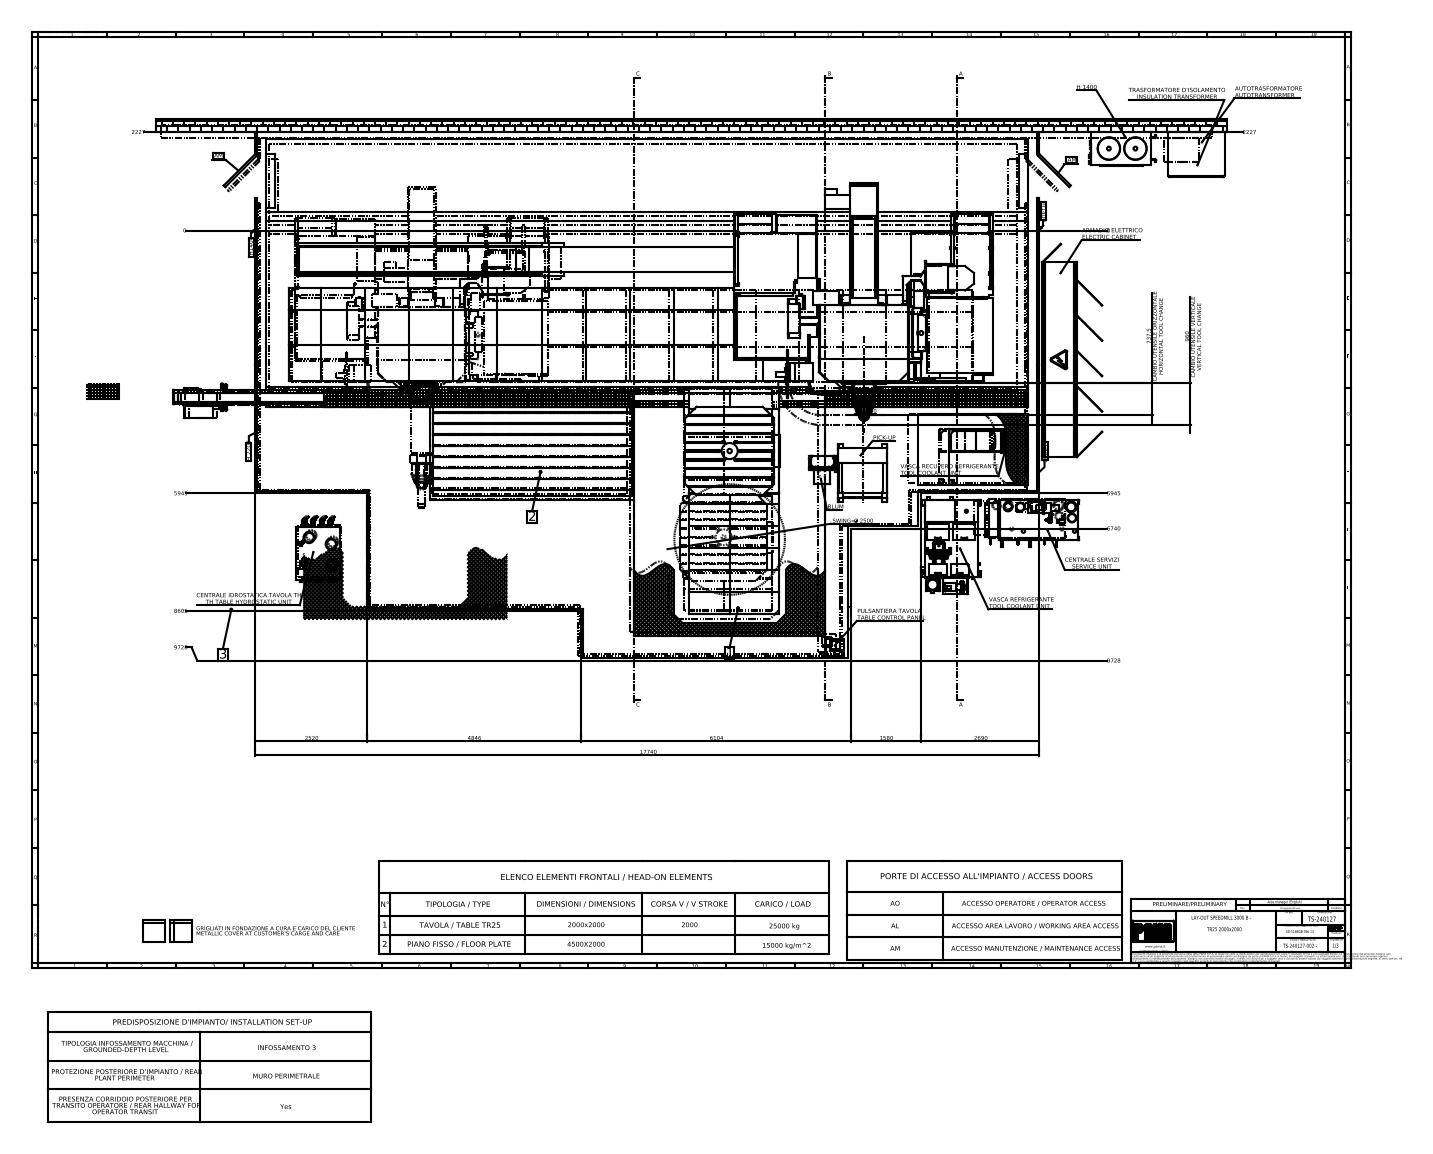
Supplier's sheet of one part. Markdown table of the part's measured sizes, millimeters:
| quantity | value |
| --- | --- |
| part name | S003552_X=MIN; Y=MIN; Z=MIN; W=MIN; S003085_Lato PO - Inf. 2-3; S001797_2000x2000 (PASSO CAVA = 200) SM. 250x250; S003390 (+8 more) |
| STEP written by | SolidWorks 2023 (AUTOMOTIVE_DESIGN) |
| units | millimeters |
| bodies | 448 solids, 6485 faces (5053 planar, 1070 cylindrical, 362 other) |
| overall size | 24240 × 15205 × 9400 |
| volume | 706 900 000 000 mm³ |
| surface area | 2 452 000 000 mm² |
| round holes (diameter × count) | 35 × 118, 69.6 × 63, 8 × 6, 32 × 6, 14 × 4, 50 × 3, 15 × 2, 19 × 2, 81 × 2, 85 × 2, 352 × 2, 72 × 1 |
| round bosses / shafts (diameter × count) | 55 × 8, 30 × 8, 60 × 6, 35 × 6, 80 × 4, 200 × 3, 174 × 3, 12 × 3 |
| partial cylindrical surfaces (radius × count) | 5 × 83, 6 × 36, 15 × 31, 35 × 24, 10 × 21, 24 × 14, 2 × 12, 25 × 12 |
| main face-to-face distances | 2000, 300, 50, 980, 1020, 15205, 14905, 660, 24240, 80 |
| hole center spacings | 250, 500, 750, 1000, 1250, 1500, 1750, 2000 |
